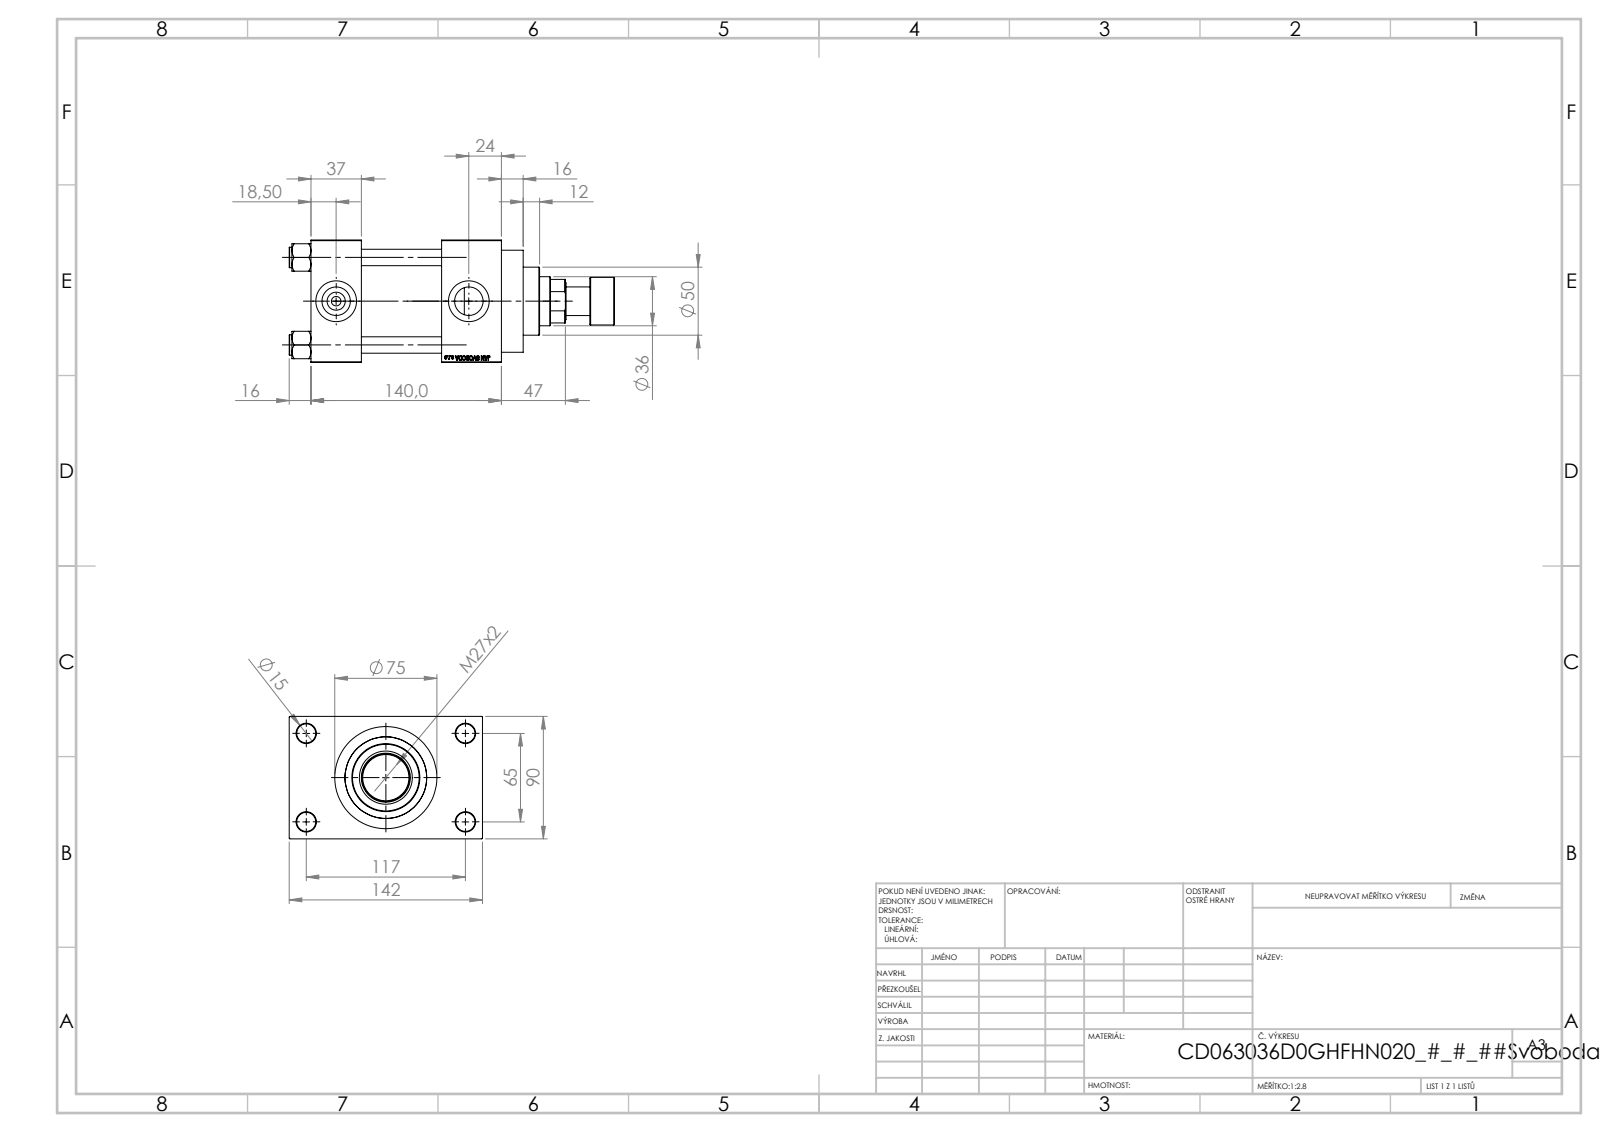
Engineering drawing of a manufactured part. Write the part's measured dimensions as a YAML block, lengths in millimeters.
part_name: "V215CR_ROD_END_F; V215CD_VC_A; V215CD_VCP_D; V215CD_D_Body (+2 more)"
step_written_by: "SolidWorks 2019 (CONFIG_CONTROL_DESIGN)"
units: millimeters
bodies: {solids: 12, faces: 1117, planar: 501, cylindrical: 92, other: 524}
overall_size: [239, 142, 90]
volume: 1135000
surface_area: 211351
round_holes:
  - {diameter: 12, count: 4}
  - {diameter: 14, count: 4}
  - {diameter: 7, count: 2}
  - {diameter: 20.96, count: 2}
  - {diameter: 30, count: 2}
  - {diameter: 25.5, count: 1}
  - {diameter: 36, count: 1}
  - {diameter: 39, count: 1}
  - {diameter: 50, count: 1}
  - {diameter: 60, count: 1}
  - {diameter: 63, count: 1}
round_bosses_or_shafts:
  - {diameter: 15, count: 4}
  - {diameter: 75, count: 1}
  - {diameter: 69, count: 1}
  - {diameter: 35, count: 1}
  - {diameter: 21, count: 1}
face_to_face_distances: [90, 59, 37, 96, 140, 103, 44, 26, 116, 142]
hole_center_spacings: [26.35, 45.47, 64.3, 66.92, 69.81, 90.65, 111.34, 65]
